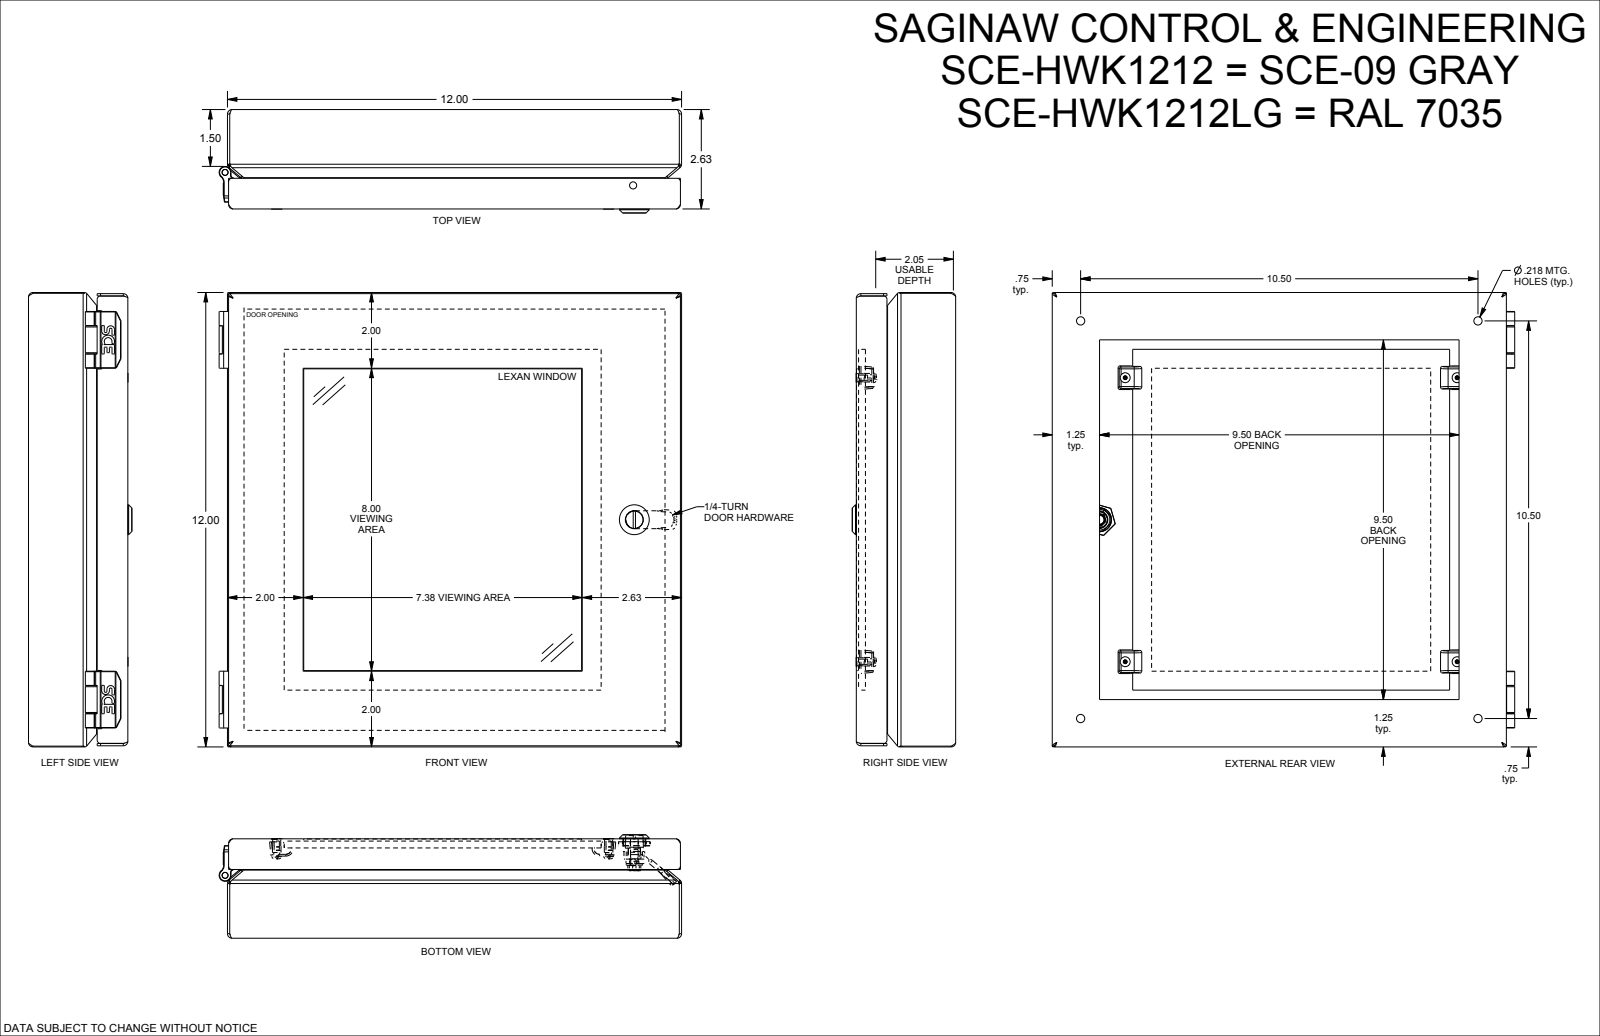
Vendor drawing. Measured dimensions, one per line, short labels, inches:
name: SCE-HWK1212LG
written by: SolidWorks 2021 (AUTOMOTIVE_DESIGN)
unit: in
bodies: 25 solids, 938 faces (361 planar, 353 cylindrical, 224 other)
size: 12.22 × 12.03 × 2.732
volume: 37.74 in³; area: 806.4 in²
holes: 4× ⌀0.138, 4× ⌀0.156, 4× ⌀0.213, 4× ⌀0.218, 2× ⌀0.02, 2× ⌀0.1, 1× ⌀0.158, 1× ⌀0.196, 1× ⌀0.2, 1× ⌀0.326, 1× ⌀0.475
bosses: 4× ⌀0.262, 4× ⌀0.212, 2× ⌀0.26, 2× ⌀0.18, 1× ⌀0.788, 1× ⌀0.548, 1× ⌀0.46, 1× ⌀0.35
rounds: 32× R0.008, 30× R0.05, 28× R0.03, 21× R0.013, 10× R0.06, 8× R0.01, 7× R0.2, 6× R0.102
face distances: 0.059, 0.06, 0.181, 0.241, 11.941, 0.236, 0.055, 12, 2.384, 2.565
hole spacings: 0.03, 7.5, 8.77, 10.5, 11.54, 1.598, 1.907, 3.811
